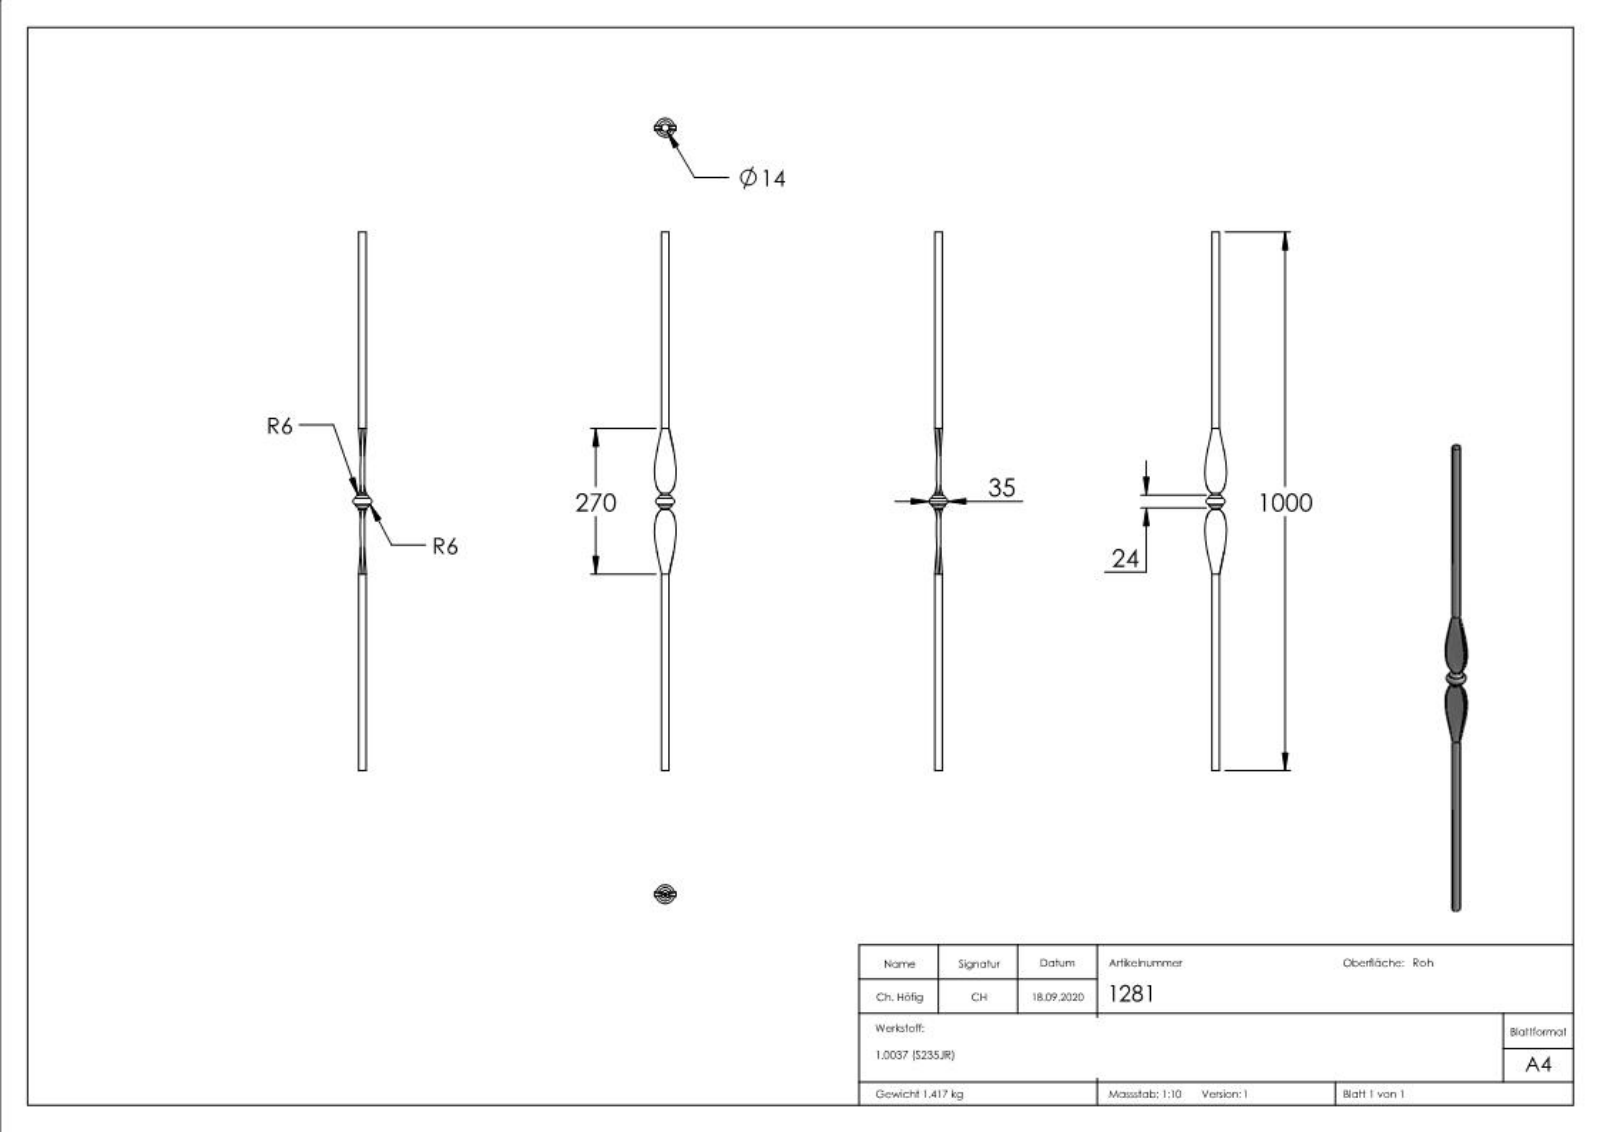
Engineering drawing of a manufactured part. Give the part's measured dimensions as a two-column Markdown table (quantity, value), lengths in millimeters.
| quantity | value |
| --- | --- |
| part name | 1281 |
| STEP written by | SolidWorks 2018 (CONFIG_CONTROL_DESIGN) |
| units | millimeters |
| bodies | 1 solid, 188 faces (91 planar, 12 cylindrical, 85 other) |
| overall size | 1000 × 39.91 × 35 |
| volume | 181 648 mm³ |
| surface area | 53 849 mm² |
| round bosses / shafts (diameter × count) | 25 × 1, 14 × 1 |
| main face-to-face distances | 1000, 999.9, 1.78, 2.32, 1.62, 0.83, 3.03, 0.99, 0.41, 2.25 |
